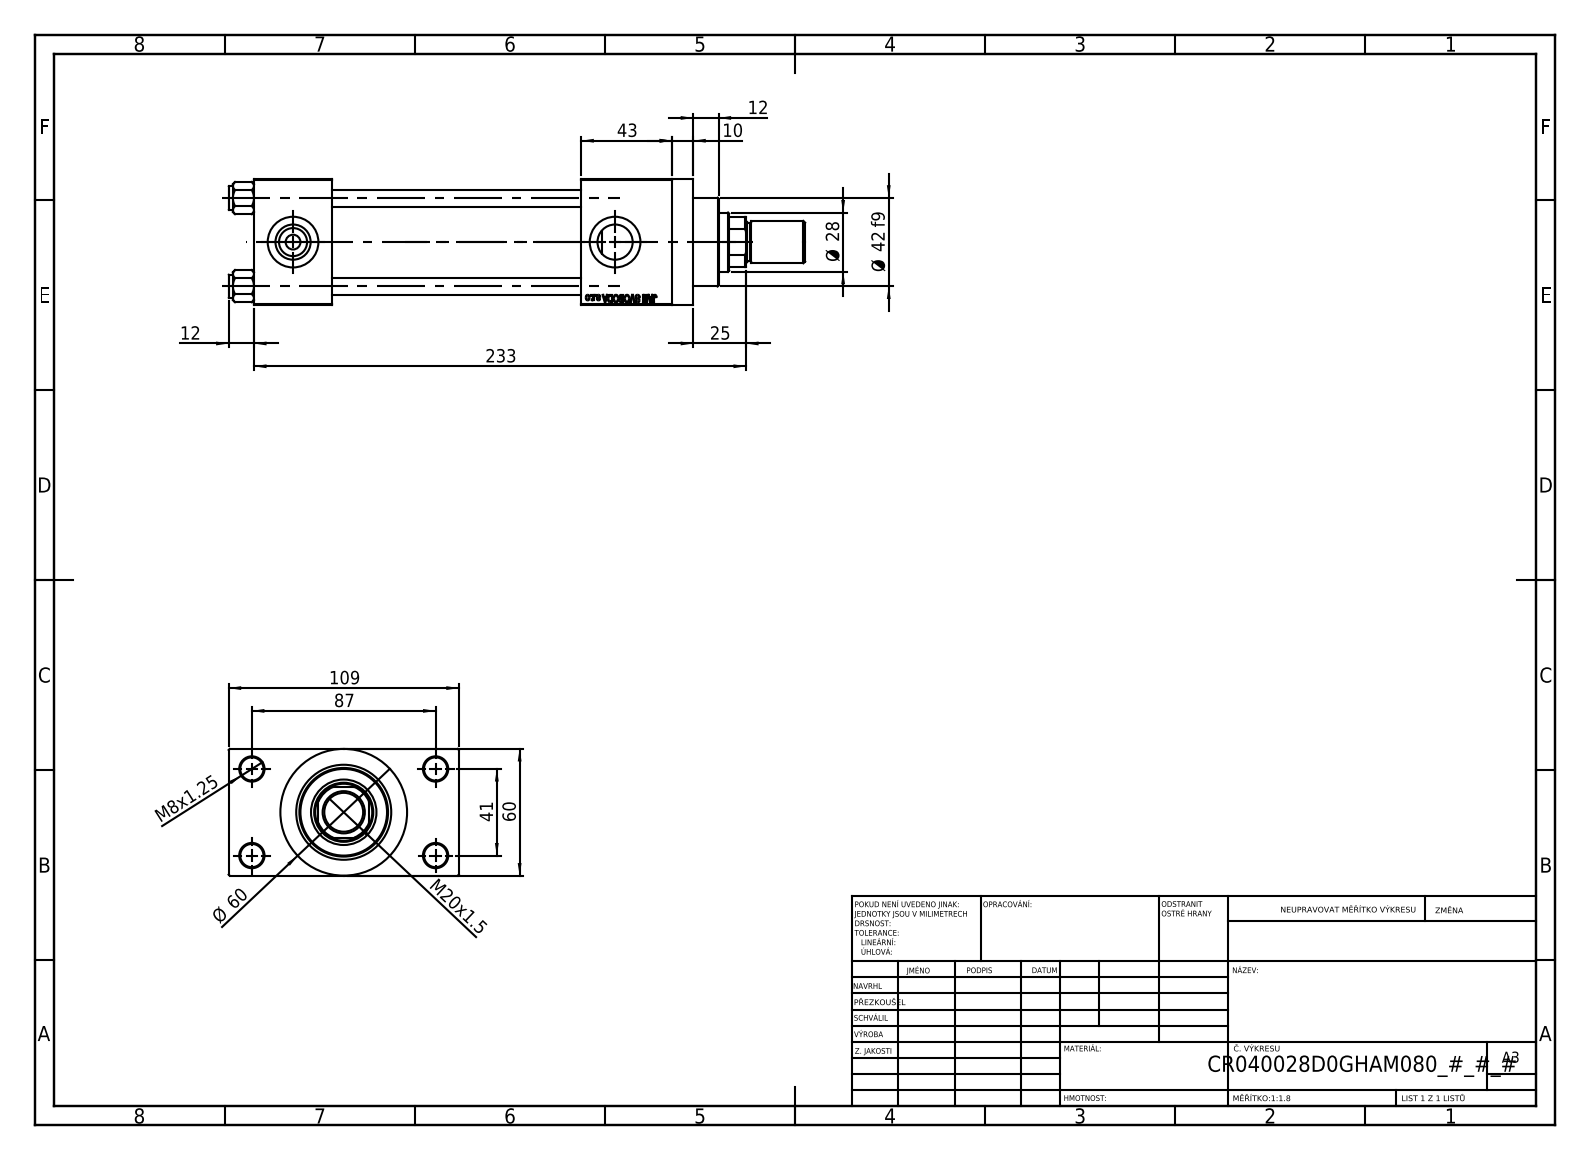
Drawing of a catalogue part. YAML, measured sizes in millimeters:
part_name: "V215CR_D_Body; ROD_END_AH; V215_VC_A; V215CR_VCP_D (+2 more)"
step_written_by: "SolidWorks 2019 (CONFIG_CONTROL_DESIGN)"
units: millimeters
bodies: {solids: 12, faces: 1118, planar: 502, cylindrical: 92, other: 524}
overall_size: [273, 109, 60]
volume: 610854
surface_area: 159060
round_holes:
  - {diameter: 8, count: 4}
  - {diameter: 11, count: 4}
  - {diameter: 7, count: 2}
  - {diameter: 16.66, count: 2}
  - {diameter: 24, count: 2}
  - {diameter: 18.5, count: 1}
  - {diameter: 28, count: 1}
  - {diameter: 31, count: 1}
  - {diameter: 40, count: 1}
  - {diameter: 45, count: 1}
round_bosses_or_shafts:
  - {diameter: 11, count: 4}
  - {diameter: 60, count: 1}
  - {diameter: 46, count: 1}
  - {diameter: 42, count: 1}
  - {diameter: 20, count: 1}
  - {diameter: 18, count: 1}
partial_cylinders:
  - {radius: 13.5, count: 1}
face_to_face_distances: [60, 118, 24.5, 84.5, 37, 155, 198, 161, 43, 109]
hole_center_spacings: [22.65, 29.49, 41.7, 47.15, 48.09, 64.35, 76.49, 41]
